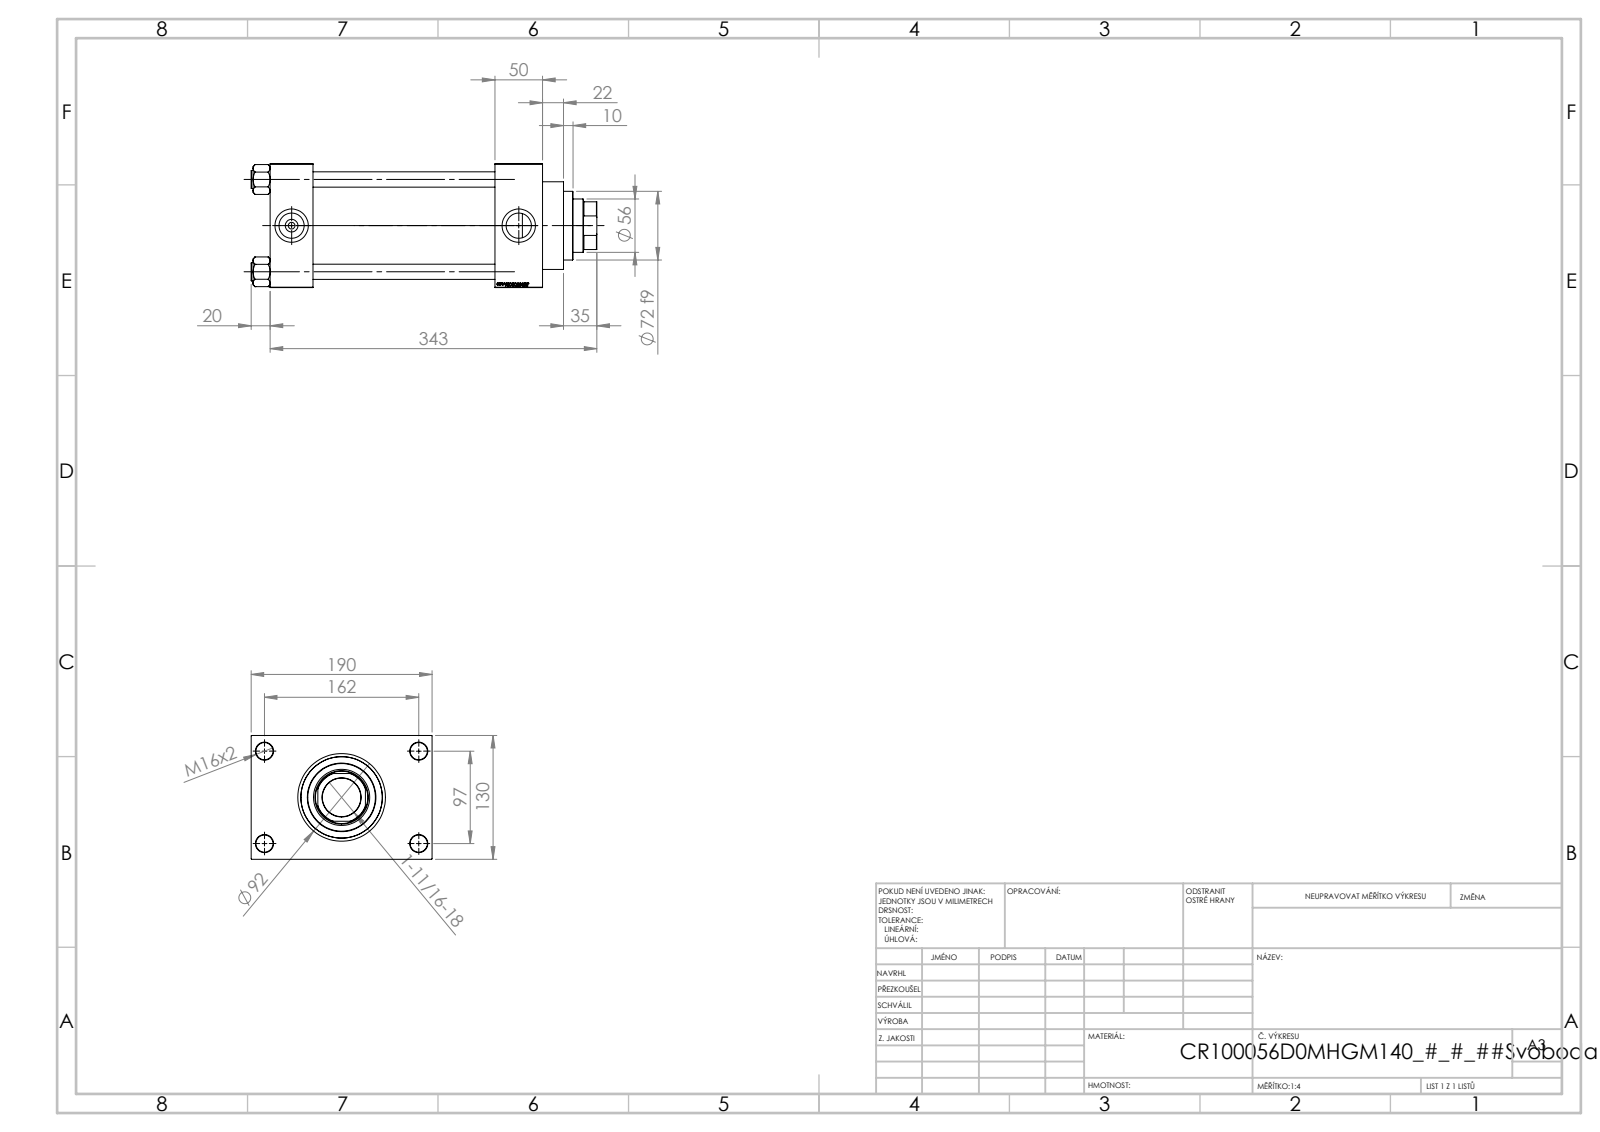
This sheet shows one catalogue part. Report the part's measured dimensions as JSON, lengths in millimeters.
{"part_name": "V215CR_D_TYCINKA; V215_VC_A; NUT_M5_D; V215CR_D_Body (+1 more)", "step_written_by": "SolidWorks 2019 (CONFIG_CONTROL_DESIGN)", "units": "millimeters", "bodies": {"solids": 11, "faces": 1151, "planar": 545, "cylindrical": 88, "other": 518}, "overall_size": [363, 190, 130], "volume_mm3": 3137000, "surface_area_mm2": 485262, "round_holes": [[16, 4], [18, 4], [7, 2], [26.44, 2], [35, 2], [40.5, 1], [56, 1], [59, 1], [76, 1], [85.5, 1], [100, 1]], "round_bosses_or_shafts": [[19, 4], [106, 1], [92, 1], [72, 1]], "partial_cylinders_radius": [[27, 1]], "face_to_face_distances": [130, 50, 45, 236, 191, 286, 241, 30, 190, 160], "hole_center_spacings": [32.55, 68.52, 94.41, 96.9, 102.27, 129.45, 161.73, 97]}
